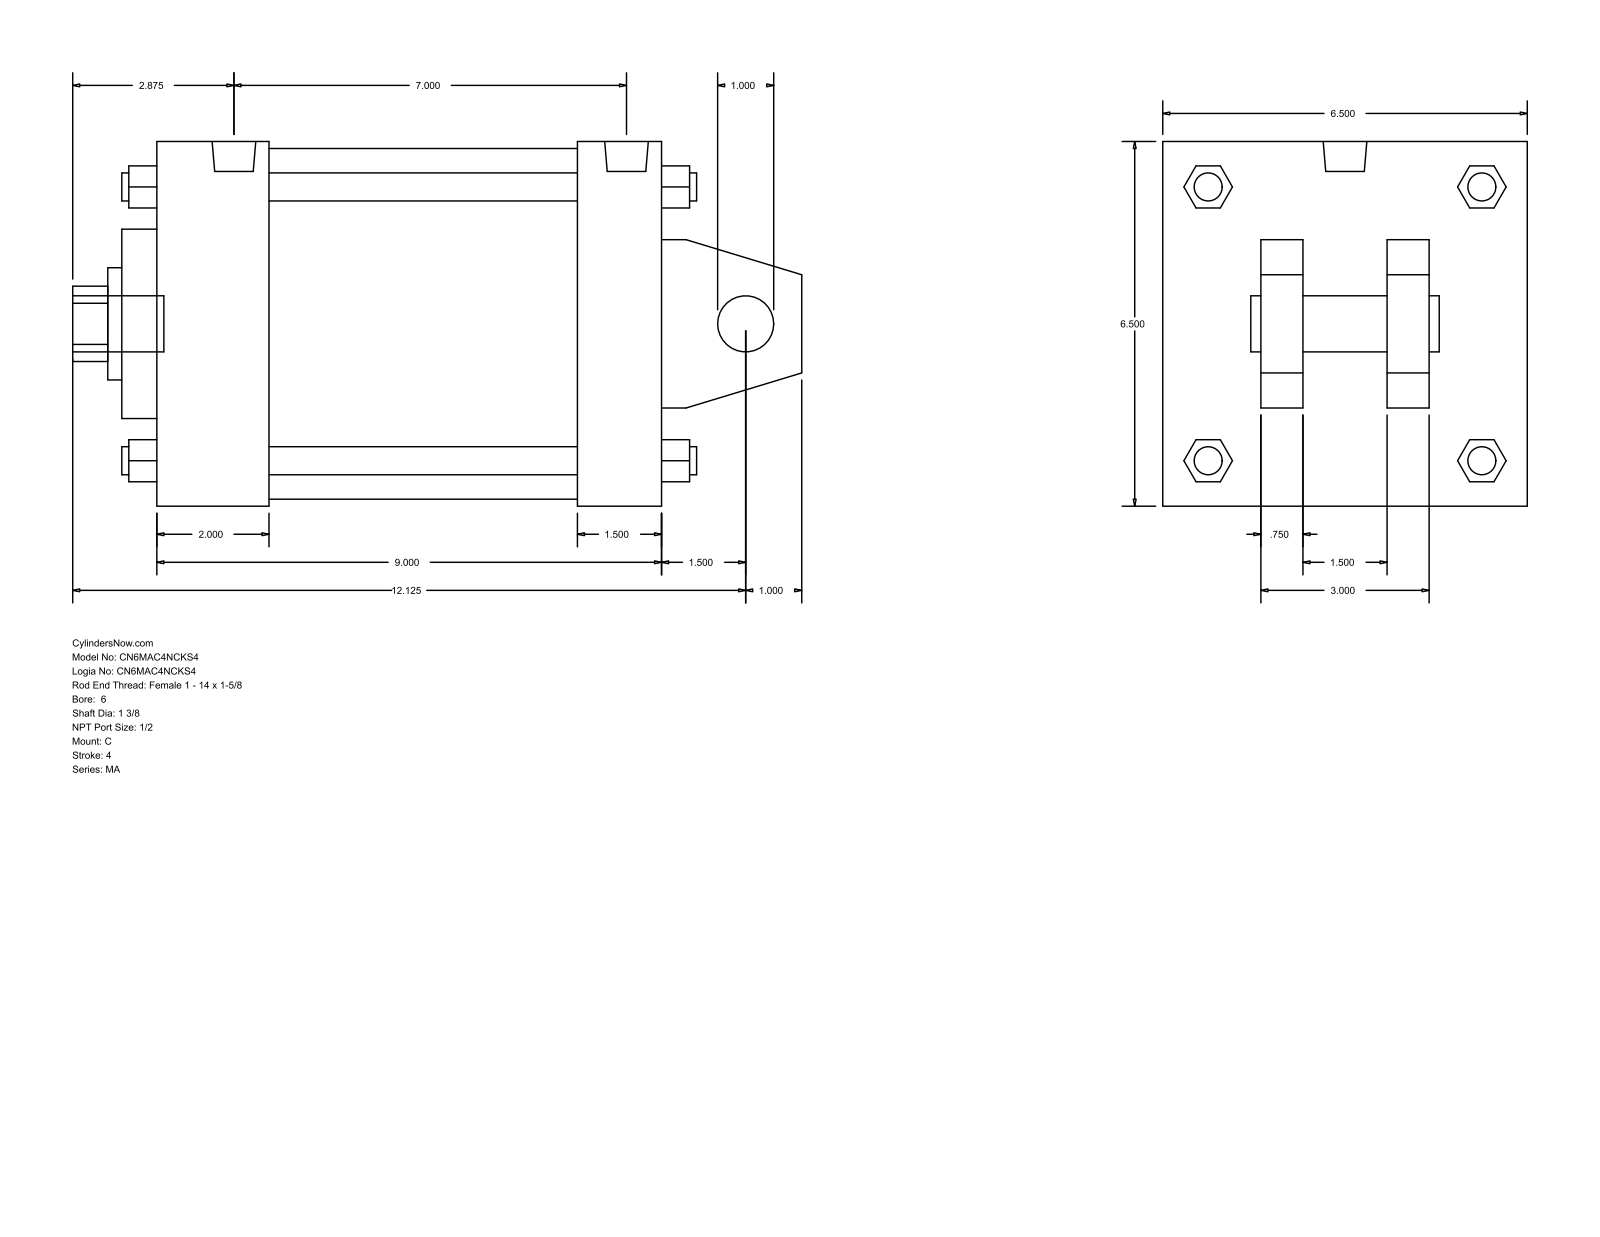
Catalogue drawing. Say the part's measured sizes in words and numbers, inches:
The part is named "MA_C__0600_1.375". Its 3-D file was written by "GSSL Pune (CONFIG_CONTROL_DESIGN)". It is 0 solids with 141 faces: 109 planar, 32 cylindrical and 0 other. Overall it measures 13 by 6.5 by 6.5 inches. Round holes: 1 of diameter 1, 1 of diameter 1.375, 1 of diameter 2, 1 of diameter 3.375, 1 of diameter 6.25. Round bosses or shafts: 4 of diameter 0.687, 4 of diameter 0.5, 2 of diameter 0.778, 1 of diameter 1. Partial cylindrical surfaces (rounded edges, fillets, slot ends): 1 of radius 0.672. The main face-to-face distances are 6.5, 9, 1.5, 0.75, 2.5, 4, 2, 4.75, 1.75, 7.5.
